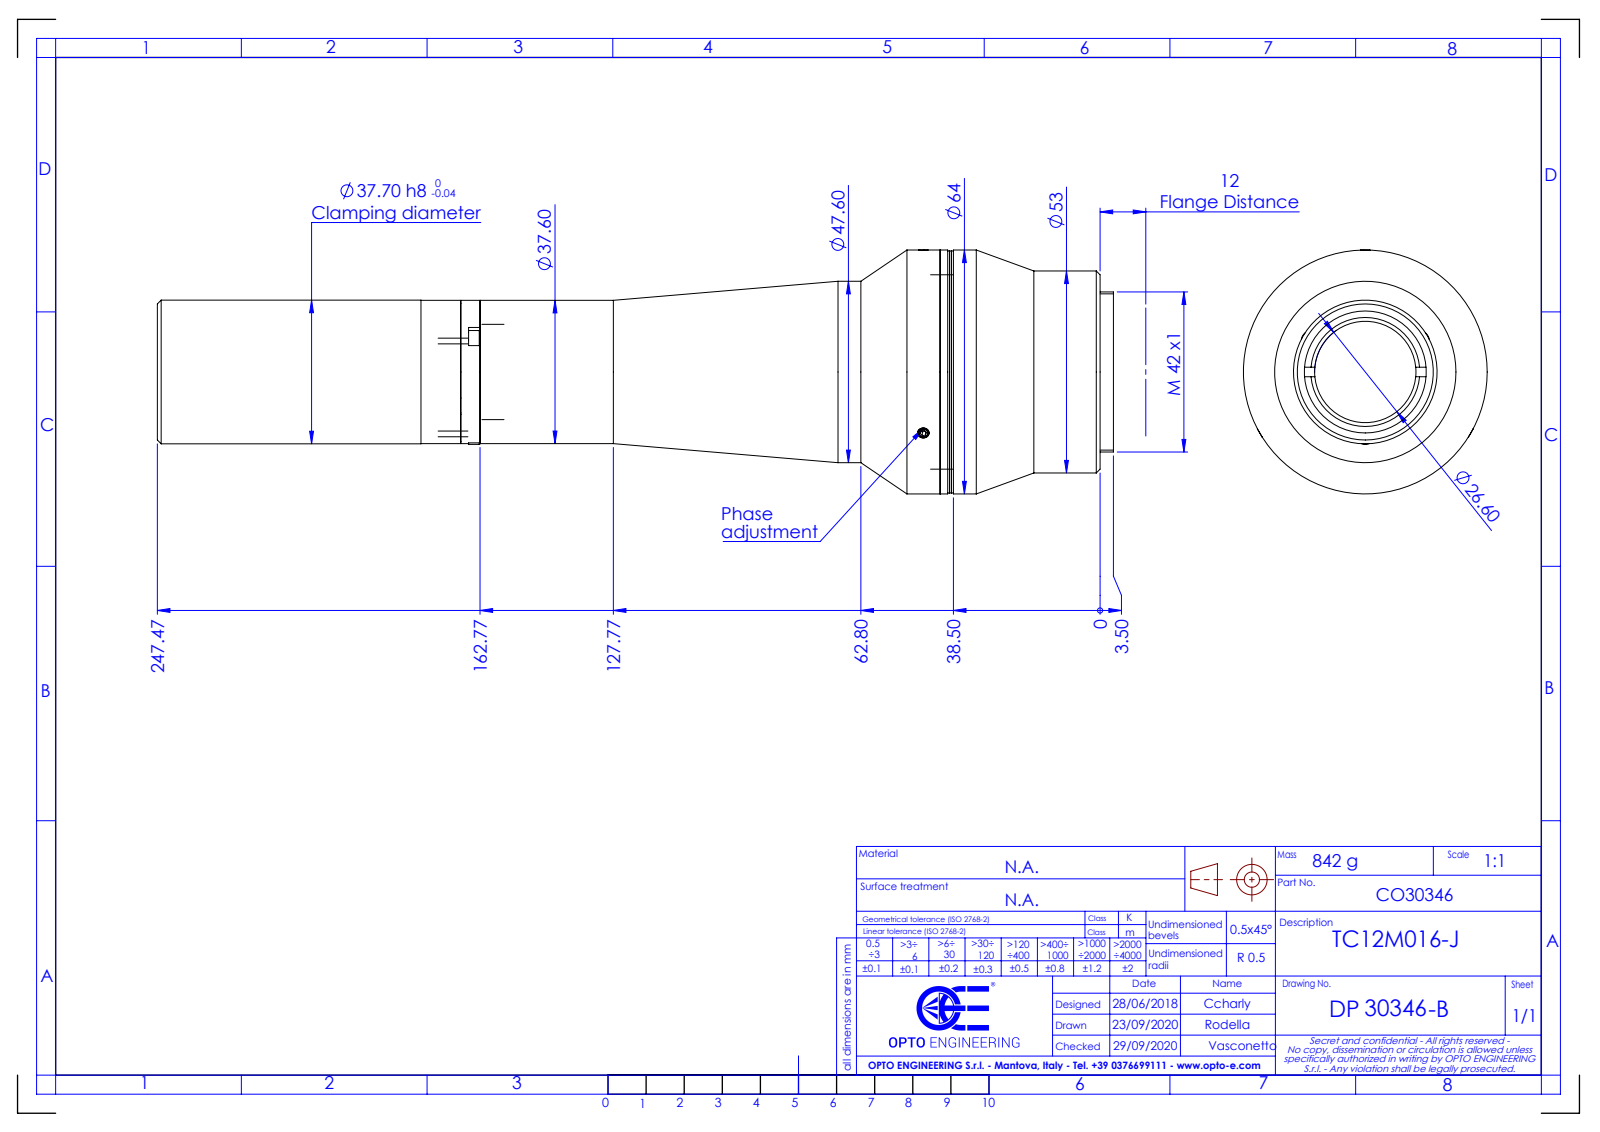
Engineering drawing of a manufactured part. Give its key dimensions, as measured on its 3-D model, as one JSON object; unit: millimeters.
{"part_name": "DP30346_TC12M016-J", "step_written_by": "SolidWorks 2021 (CONFIG_CONTROL_DESIGN)", "units": "millimeters", "bodies": {"solids": 0, "faces": 120, "planar": 52, "cylindrical": 40, "other": 28}, "overall_size": [250.97, 64, 64], "round_holes": [[26.6, 1], [32, 1], [39, 1], [45, 1]], "round_bosses_or_shafts": [[5.5, 3], [64, 1], [63.5, 1], [53, 1], [47.6, 1], [42, 1], [37.7, 1], [37.6, 1]], "face_to_face_distances": [3.5, 2, 120.77, 122.77, 1.5, 124.27, 42, 162.77, 40, 38.5]}
